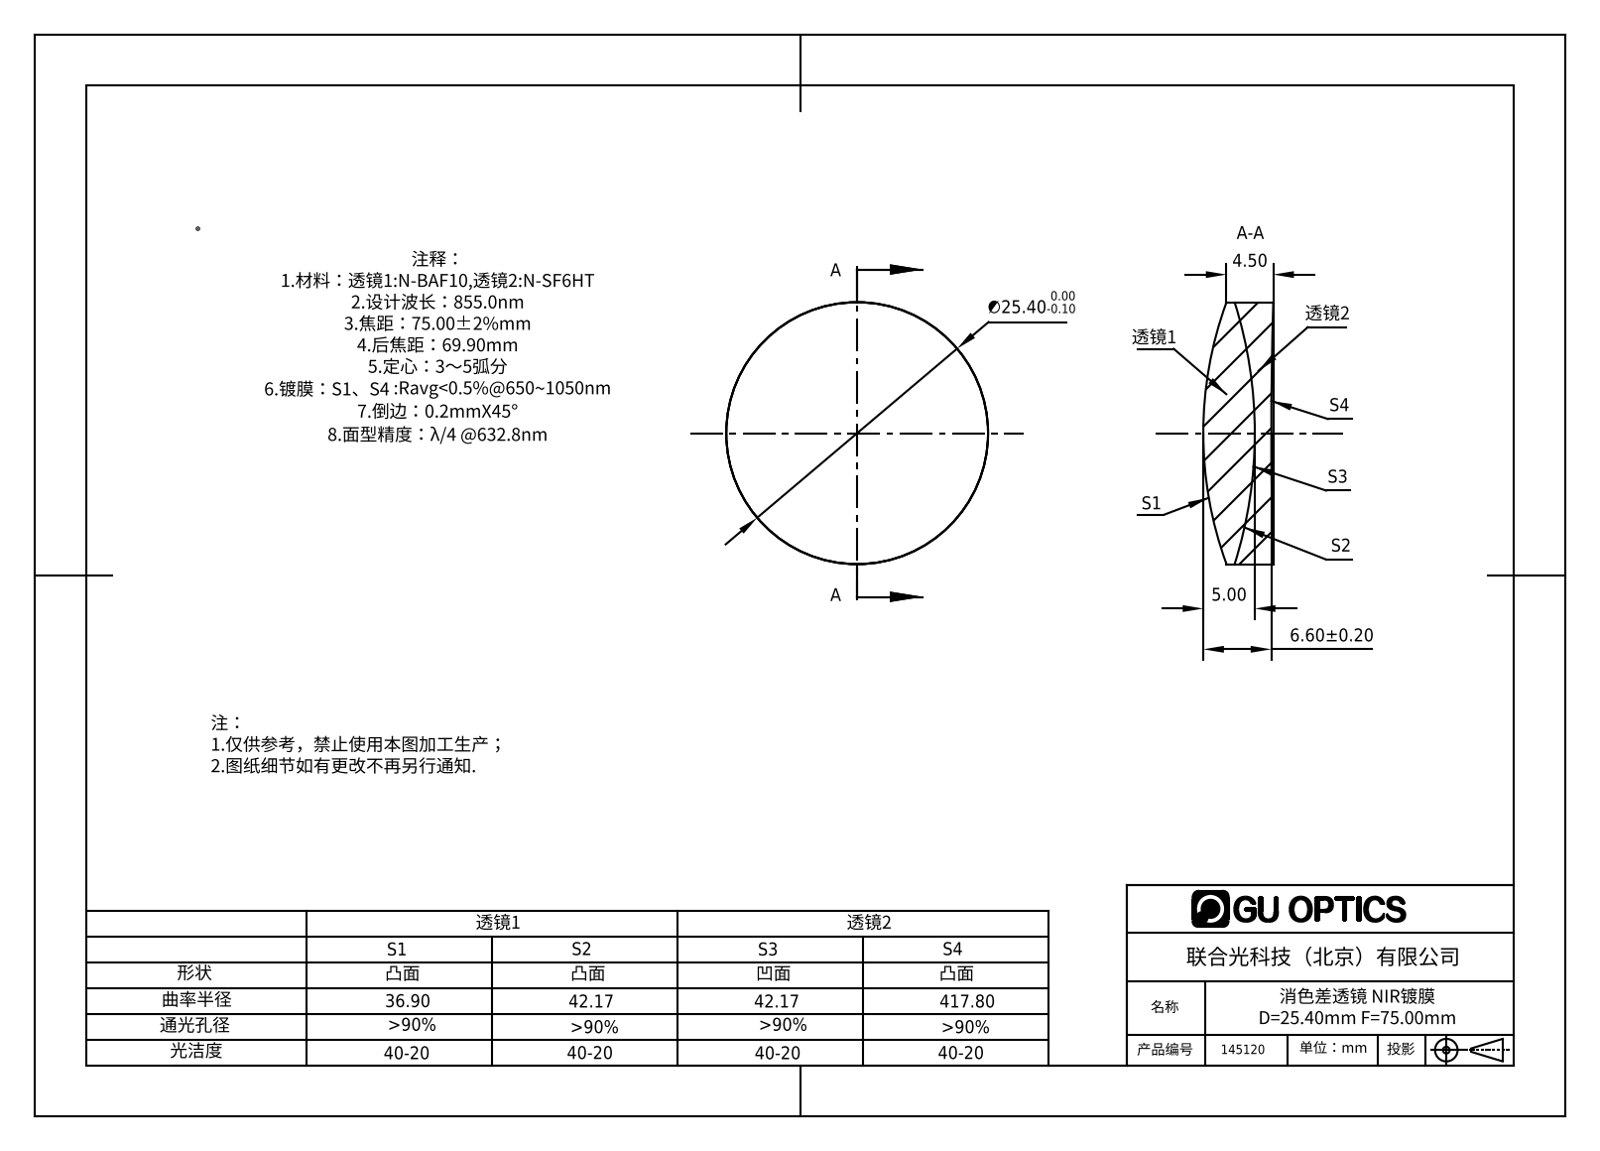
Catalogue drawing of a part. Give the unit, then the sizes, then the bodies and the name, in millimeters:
Units: millimetres
Overall size (bounding box): 25.4 × 25.4 × 6.79
Round bosses / shafts (diameter × count): ⌀25.4 ×1
Volume: 2 828 mm³ · Surface area: 2 429 mm²
Bodies: 2 solids, 12 faces (0 planar, 4 cylindrical, 8 other)
Part name (STEP PRODUCT): 145120
STEP written by: SolidWorks 2016 (AUTOMOTIVE_DESIGN)
